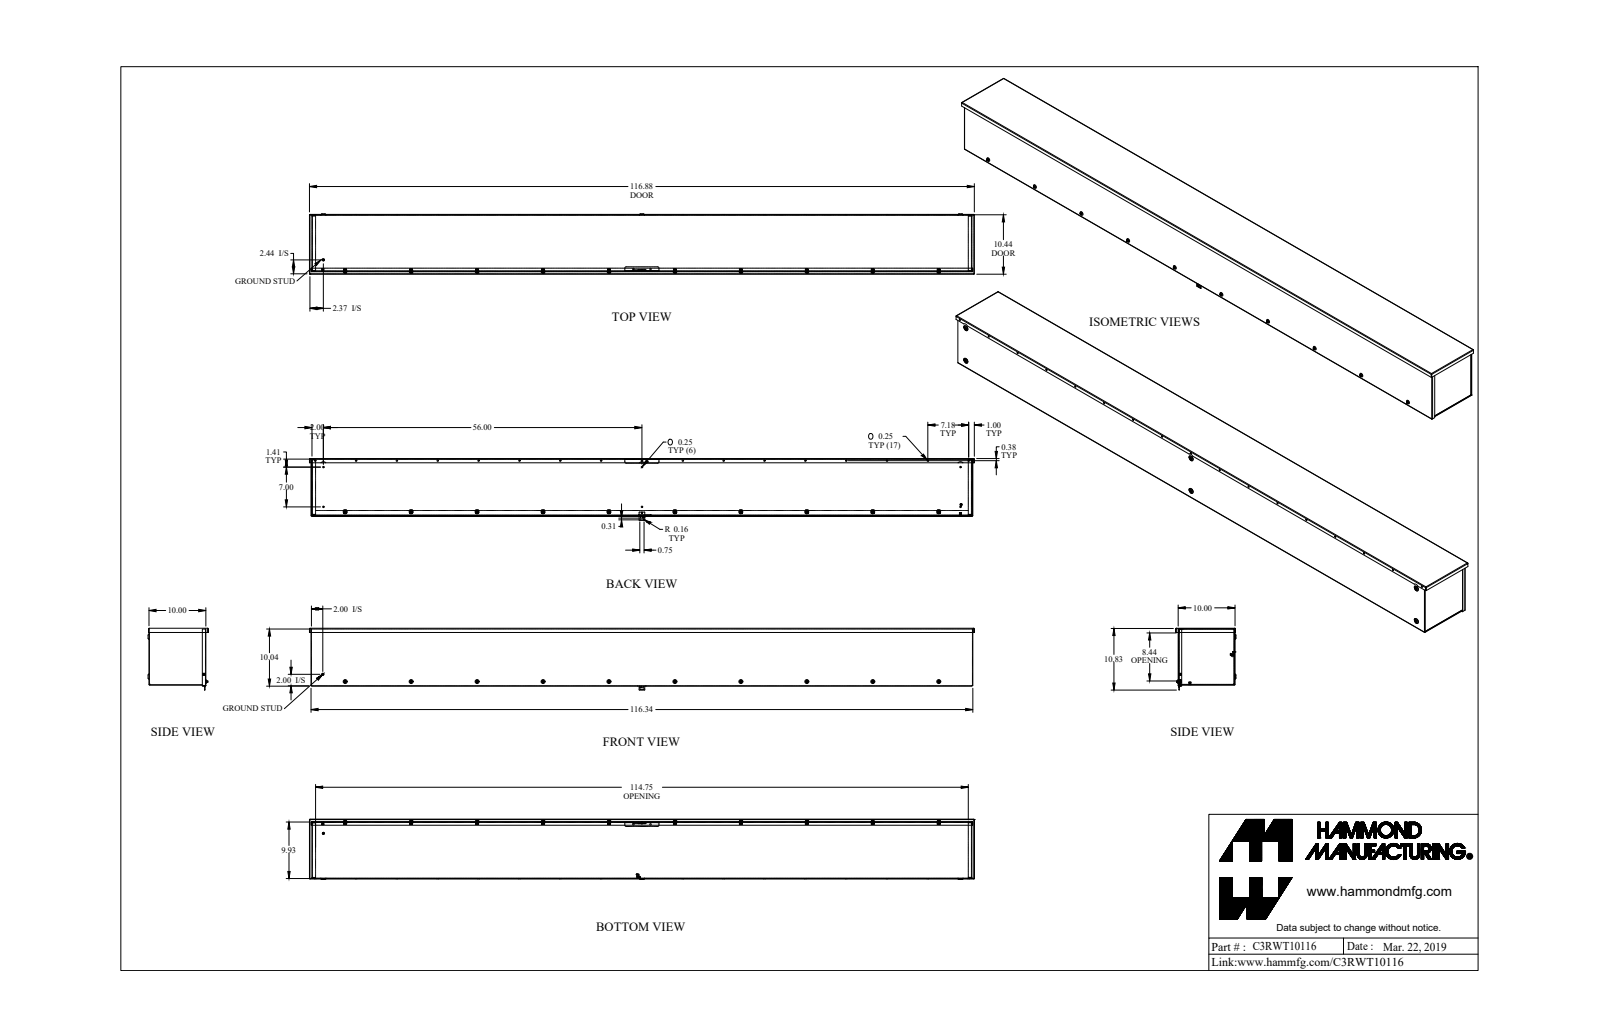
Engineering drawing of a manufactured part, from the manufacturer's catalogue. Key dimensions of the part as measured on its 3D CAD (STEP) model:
Part name (STEP PRODUCT): C3RWT10116_Default
STEP written by: SolidWorks 2019 (CONFIG_CONTROL_DESIGN)
Units: inches
Bodies: 44 solids, 1696 faces (925 planar, 547 cylindrical, 224 other)
Overall size (bounding box): 116.875 × 10.871 × 10.594
Volume: 379.1 in³ · Surface area: 10 617 in²
Round holes (diameter × count): ⌀0.25 ×25, ⌀0.156 ×12, ⌀0.214 ×10, ⌀0.23 ×10, ⌀0.203 ×2, ⌀0.125 ×1, ⌀0.137 ×1, ⌀0.2 ×1, ⌀0.215 ×1
Round bosses / shafts (diameter × count): ⌀0.19 ×11, ⌀0.148 ×10, ⌀0.375 ×2, ⌀0.5 ×1, ⌀0.367 ×1, ⌀0.21 ×1, ⌀0.152 ×1, ⌀0.125 ×1
Partial cylindrical surfaces — rounded edges, fillets, slot ends (radius × count): R0.08 ×40, R0.108 ×40, R0.022 ×20, R0.036 ×18, R0.108 ×18, R0.125 ×18, R0.171 ×10, R0.206 ×10
Main face-to-face distances: 0.072, 9.928, 10, 0.072, 9.856, 9.856, 9.928, 115.928, 0.144, 10.366
Hole centre spacings: 11.594, 14.359, 21.539, 7.18, 35.898, 56.436, 7.18, 23.187
